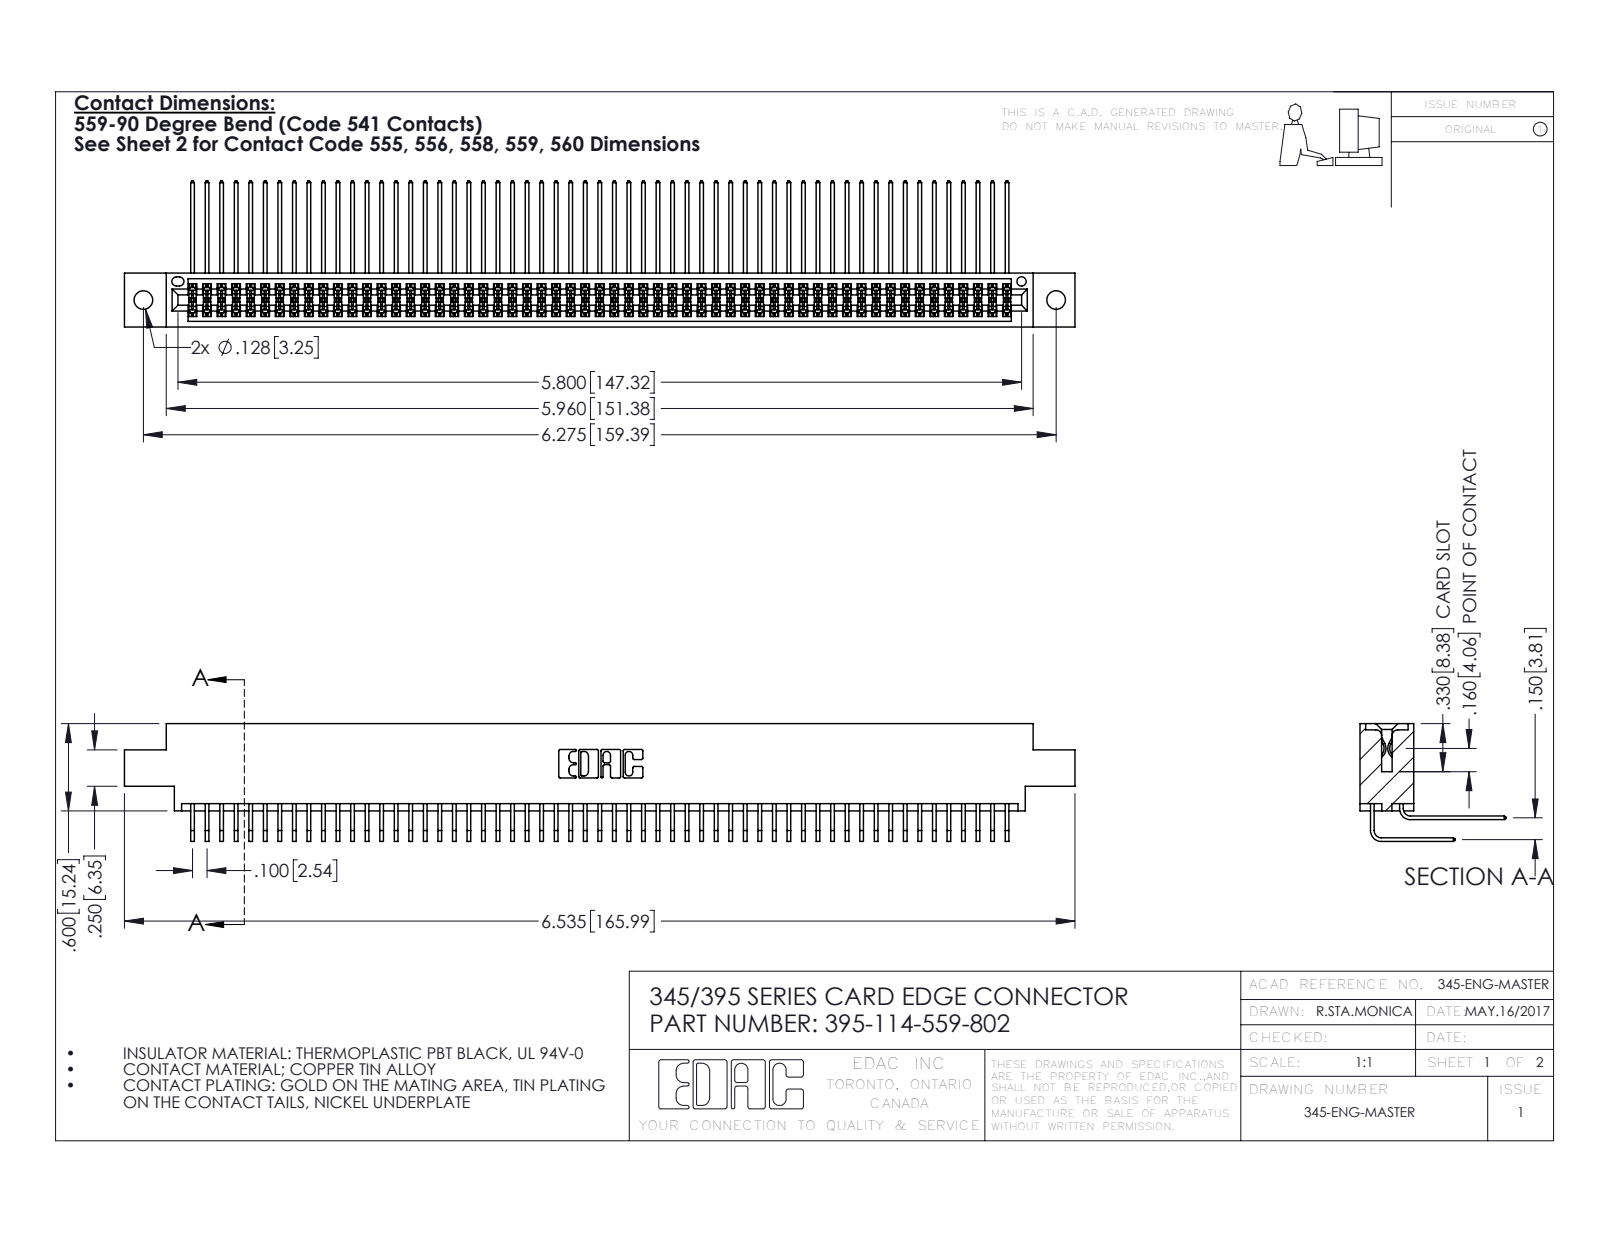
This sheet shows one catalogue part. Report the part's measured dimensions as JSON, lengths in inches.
{"part_name": "345-292-001_559 Tail - 2; 395-114-559-802; 345 Part_0.170 Offset - 0.128 Dia; 345-292-001_558 559 Tail - 1", "step_written_by": "SolidWorks 2016 (CONFIG_CONTROL_DESIGN)", "units": "inches", "bodies": {"solids": 115, "faces": 6058, "planar": 4074, "cylindrical": 1984, "other": 0}, "overall_size": [6.535, 1.005, 0.809], "volume_in3": 1.023, "surface_area_in2": 43.47, "round_holes": [[0.128, 2], [0.064, 1]], "partial_cylinders_radius": [[0.006, 171], [0.01, 22], [0.007, 6], [0.031, 6], [0.026, 3], [0.014, 2], [0.019, 2], [0.022, 2]], "face_to_face_distances": [0.072, 0.298, 0.37, 0.2, 0.098, 0.272, 0.025, 0.225, 0.175, 0.15], "hole_center_spacings": [0.27, 6.039, 6.275]}
